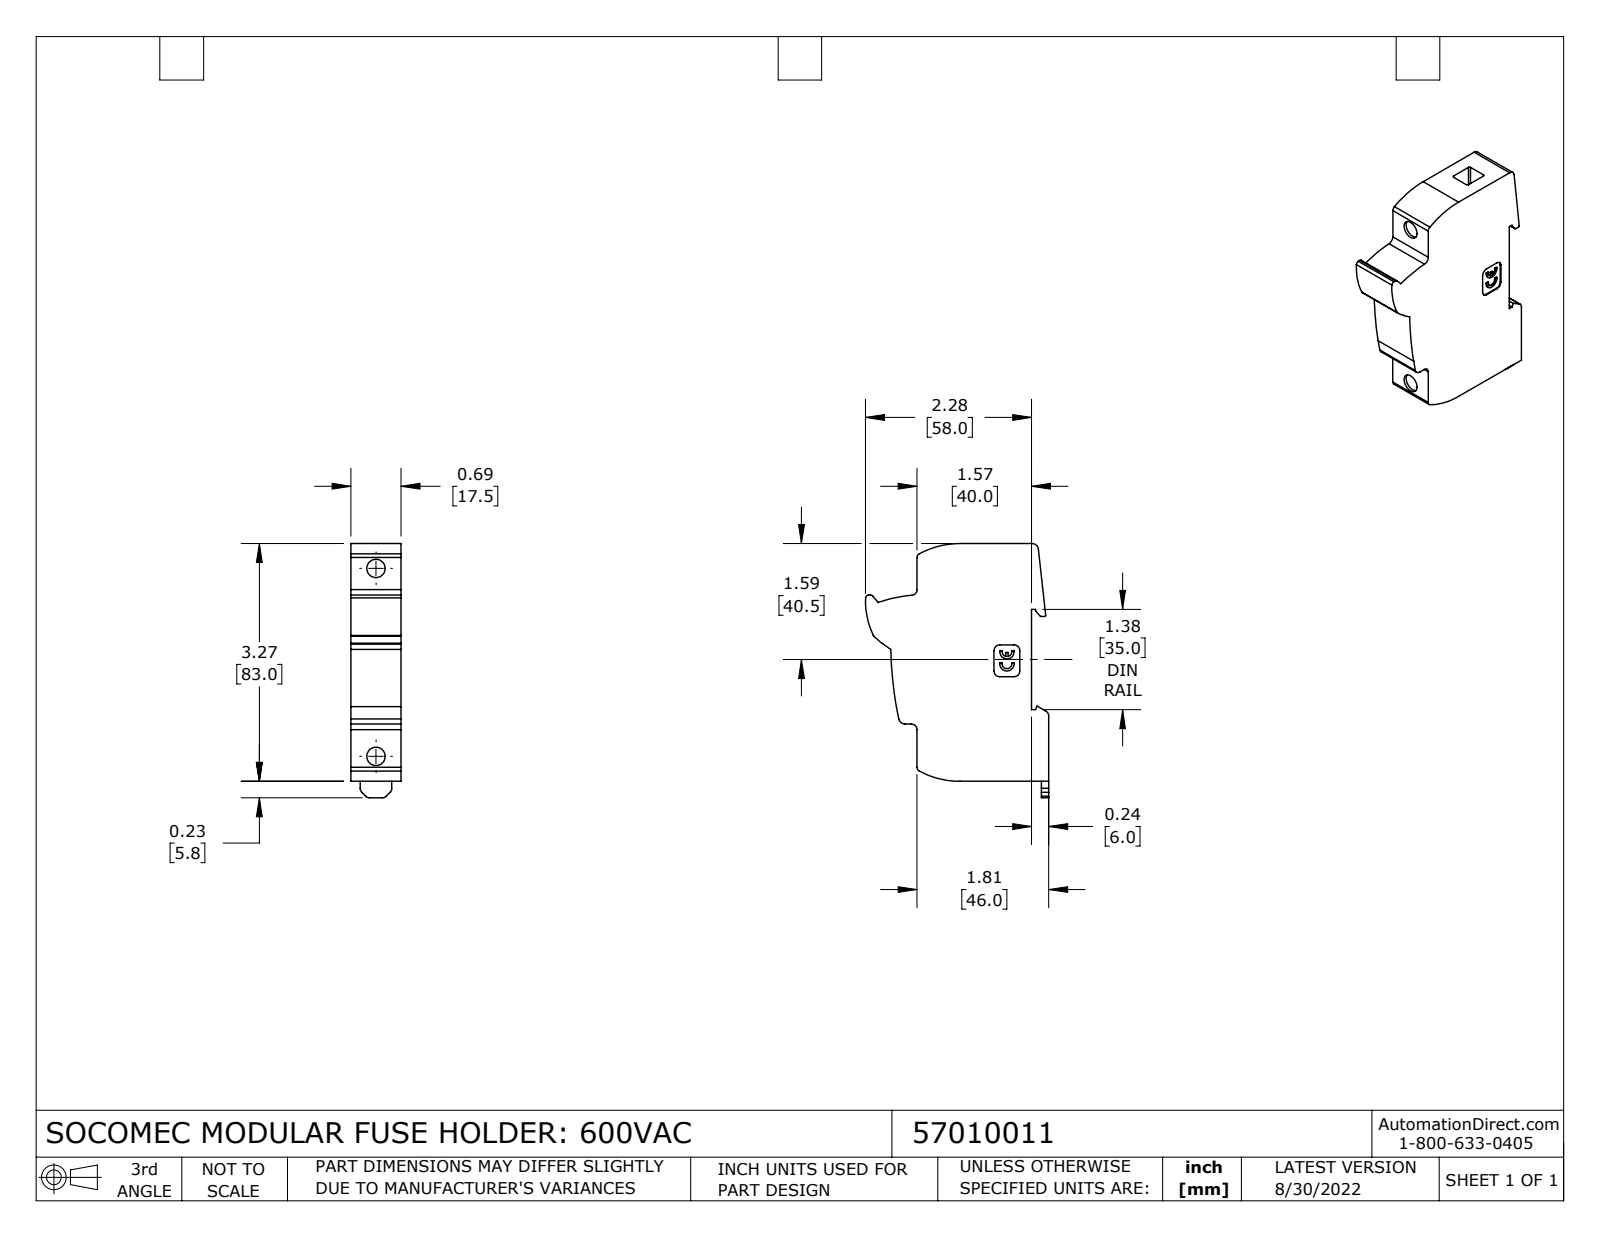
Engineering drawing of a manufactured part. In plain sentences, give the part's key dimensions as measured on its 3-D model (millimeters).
The part is named "57010011". Its 3-D file was written by "SolidWorks 2021 (CONFIG_CONTROL_DESIGN)". It is 1 solid with 105 faces: 52 planar, 53 cylindrical and 0 other. Overall it measures 88.8 by 64 by 17.5 millimeters. Its volume is 69 300 cubic millimeters and its surface area 13 760 square millimeters. Round holes: 2 of diameter 6.4. Partial cylindrical surfaces (rounded edges, fillets, slot ends): 11 of radius 2, 5 of radius 0.5, 4 of radius 1, 2 of radius 1.5, 2 of radius 1.7, 2 of radius 2.2, 2 of radius 2.5, 2 of radius 30.1. The main face-to-face distances are 17.5, 6, 40, 83, 46, 5.1, 12.4, 7.4, 13.2, 7.1. The hole center spacings are 65.6.
